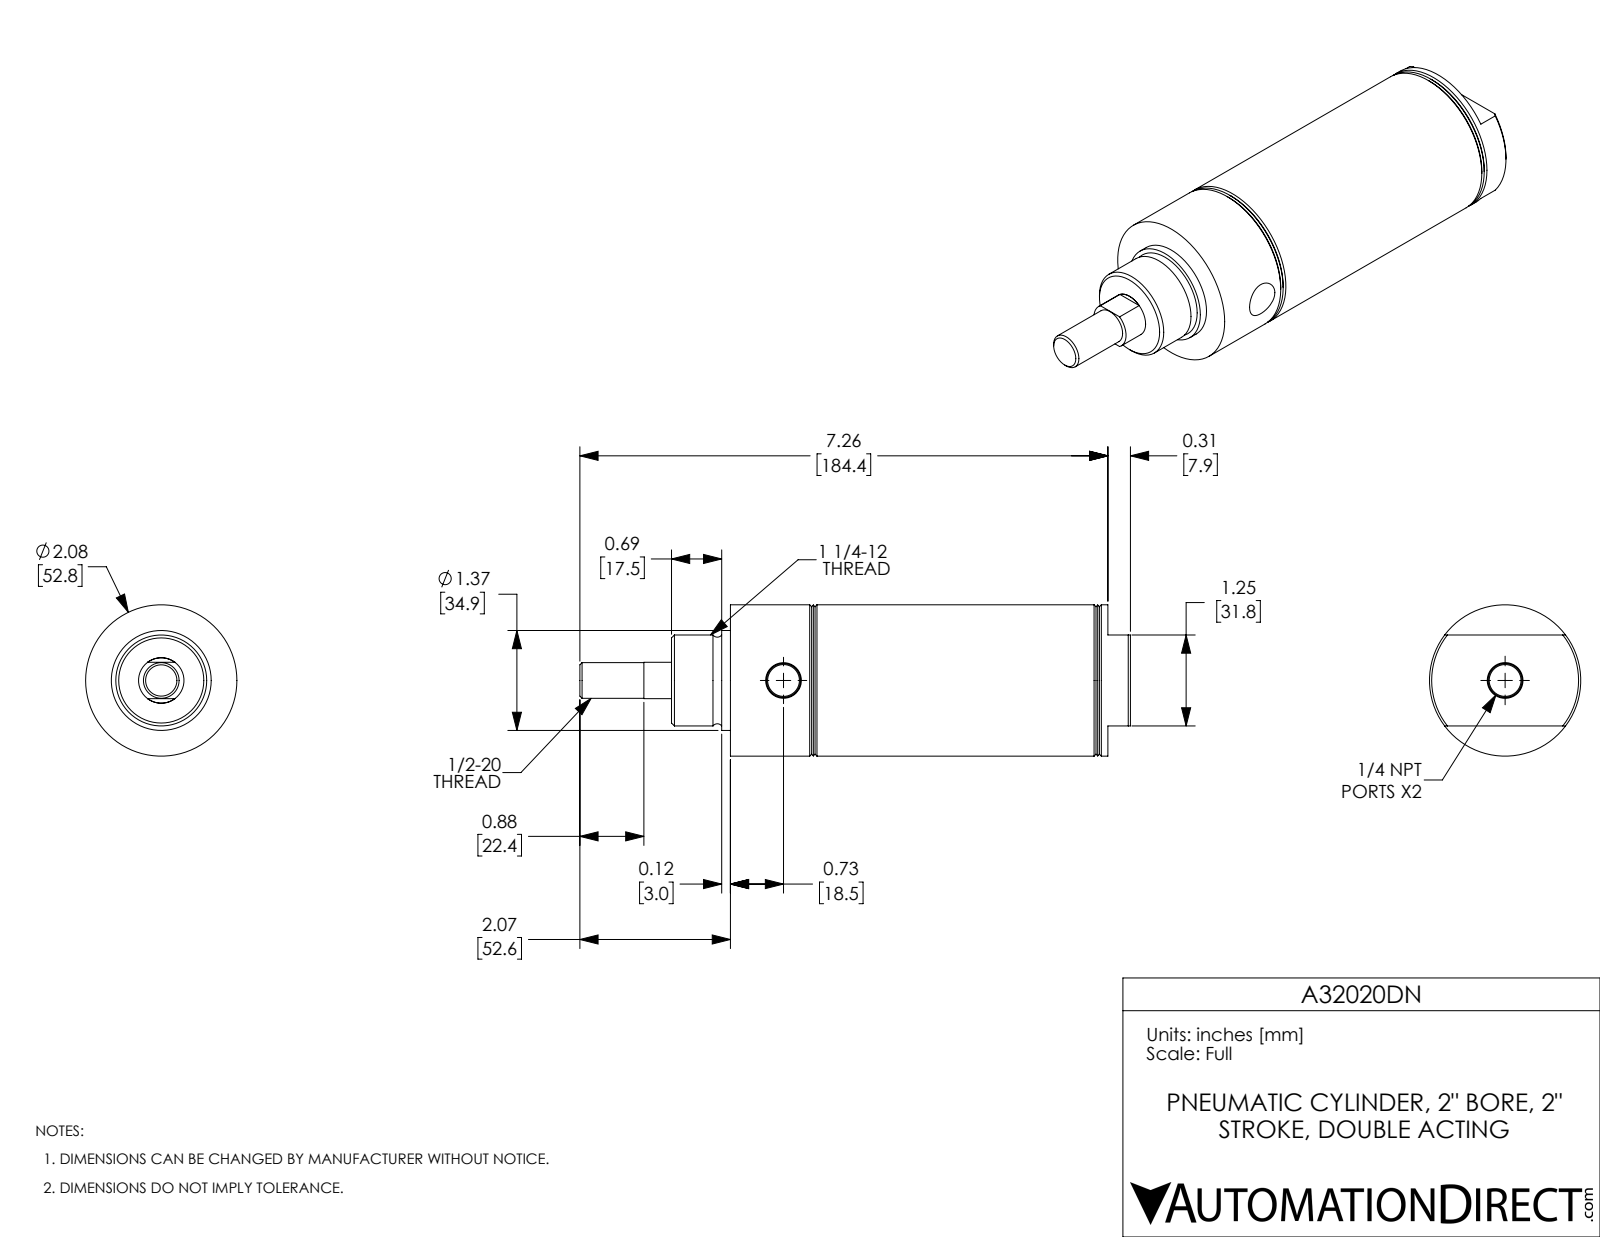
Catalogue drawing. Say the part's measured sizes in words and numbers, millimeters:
The part is named "A32020DN-MainBody; A32020DN; A32020DN-Rod". Its 3-D file was written by "SolidWorks 2017 (AUTOMOTIVE_DESIGN)". It is 2 solids with 77 faces: 20 planar, 24 cylindrical and 33 other. Overall it measures 192.3 by 52.8 by 52.8 millimeters. Its volume is 225 200 cubic millimeters and its surface area 60 540 square millimeters. Round holes: 2 of diameter 11.1, 1 of diameter 15.9, 1 of diameter 50.8. Round bosses or shafts: 1 of diameter 52.8, 1 of diameter 34.9, 1 of diameter 31.8, 1 of diameter 12.5. The main face-to-face distances are 50.8, 38.1, 101.6, 12.7, 63.5, 139.7, 88.9, 7.9, 30.2, 42.9.
